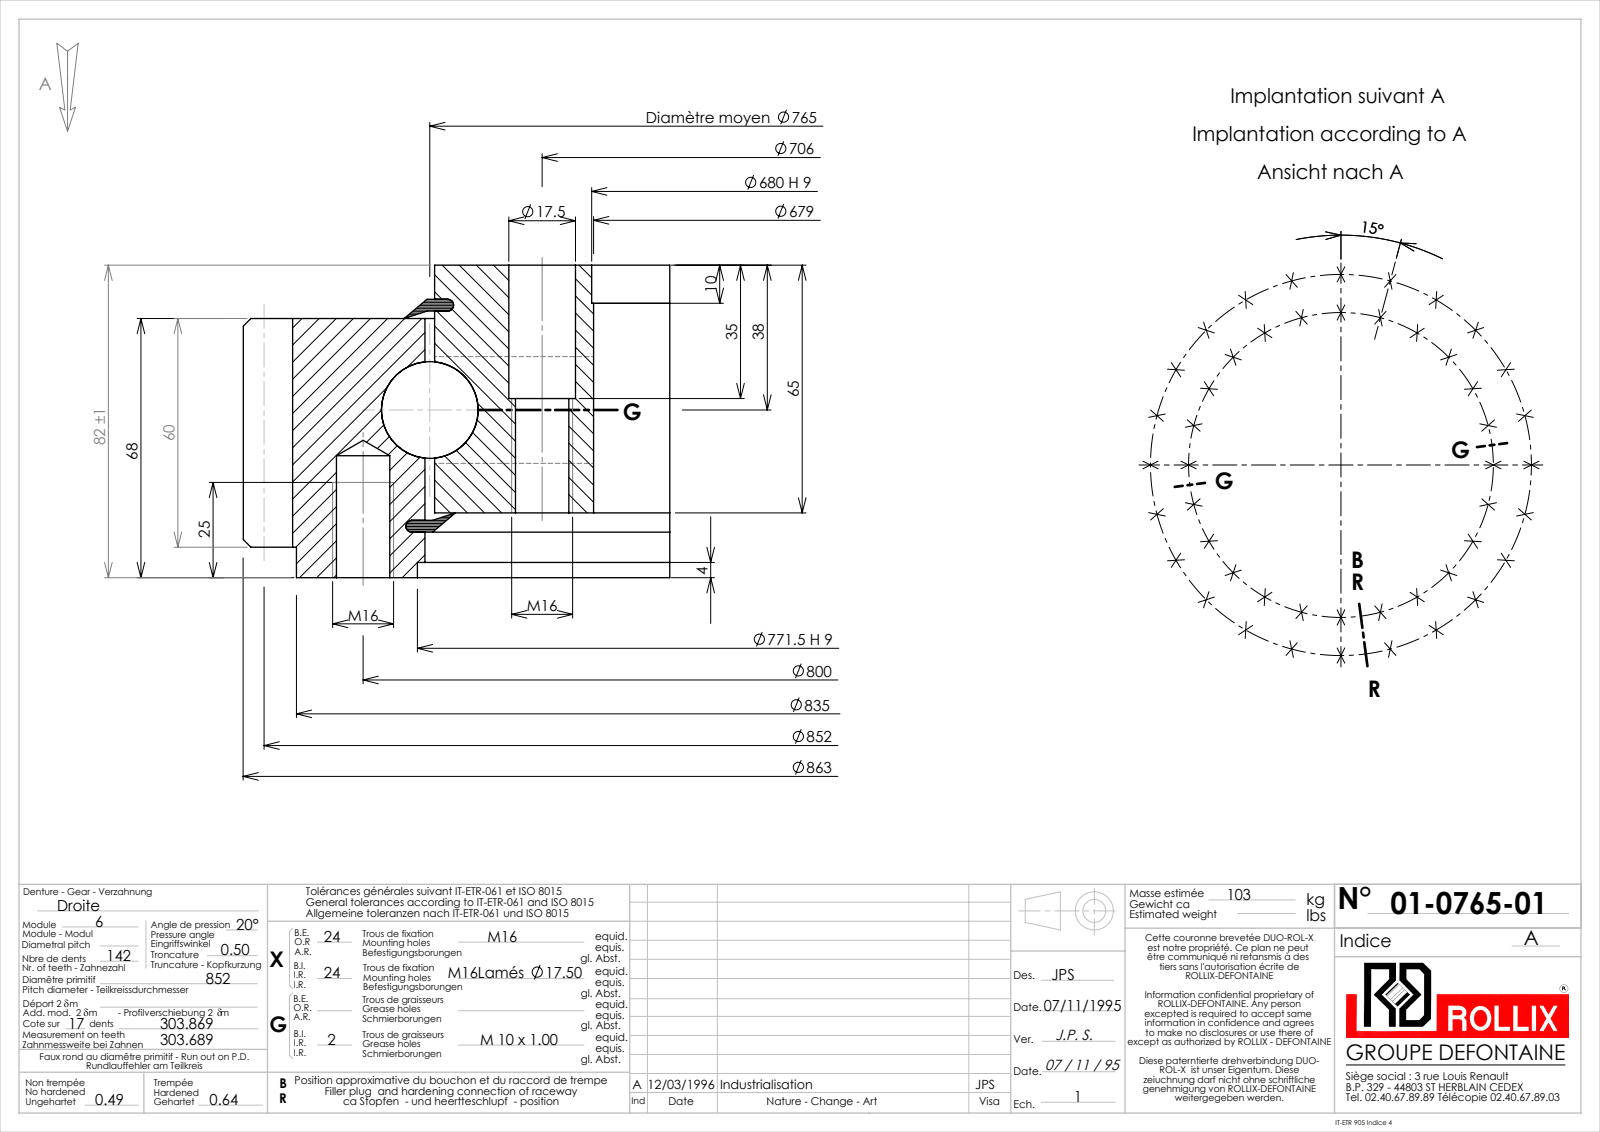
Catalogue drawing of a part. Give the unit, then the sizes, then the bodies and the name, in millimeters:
Units: millimetres
Overall size (bounding box): 863 × 862.9 × 82
Round holes (diameter × count): ⌀14 ×48, ⌀17.5 ×24, ⌀9 ×2, ⌀679 ×1, ⌀680 ×1, ⌀767.54 ×1, ⌀771.5 ×1
Round bosses / shafts (diameter × count): ⌀835 ×1, ⌀762.46 ×1
Partial cylindrical surfaces — rounded edges, fillets, slot ends (radius × count): R418.5 ×1, R431.5 ×1
Main face-to-face distances: 51, 65, 14, 68, 17, 82, 5.05, 56.05, 3.1, 1.95
Hole centre spacings: 400, 104.42, 487.01, 634.68, 692.82, 739.1, 772.74, 565.69
Volume: 11 740 000 mm³ · Surface area: 1 547 000 mm²
Bodies: 5 solids, 1136 faces (323 planar, 453 cylindrical, 360 other)
Part name (STEP PRODUCT): 01-0765-01
STEP written by: SolidWorks 2016 (CONFIG_CONTROL_DESIGN)
